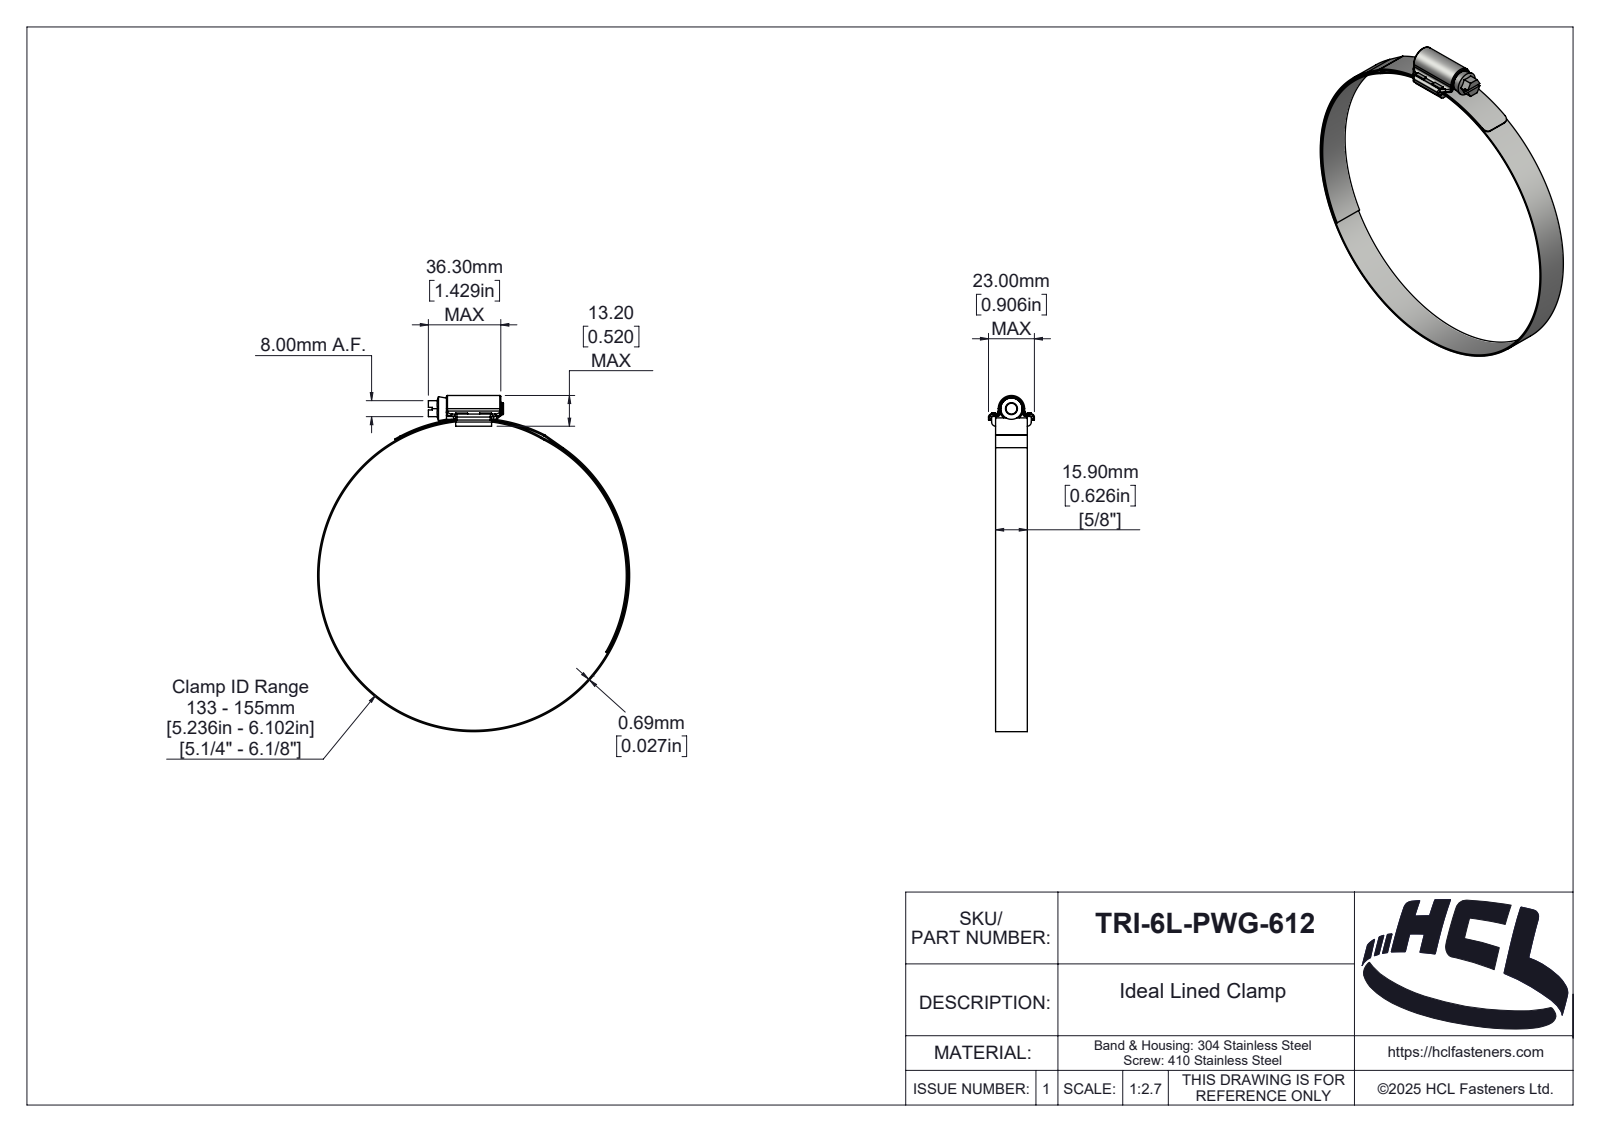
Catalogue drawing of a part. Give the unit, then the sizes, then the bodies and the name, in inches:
Units: inches
Overall size (bounding box): 6.63 × 6.157 × 0.906
Round holes (diameter × count): ⌀6.102 ×1
Round bosses / shafts (diameter × count): ⌀6.157 ×1, ⌀0.421 ×1, ⌀0.236 ×1
Partial cylindrical surfaces — rounded edges, fillets, slot ends (radius × count): R0.039 ×14, R0.02 ×4, R0.059 ×4, R0.079 ×3, R0.004 ×2, R0.083 ×2, R0.118 ×2, R0.018 ×1
Main face-to-face distances: 0.626, 0.079, 0.705, 0.027, 0.193, 0.047, 0.179, 0.132, 0.604, 0.1
Volume: 0.78 in³ · Surface area: 42.72 in²
Bodies: 4 solids, 268 faces (87 planar, 102 cylindrical, 79 other)
Part name (STEP PRODUCT): TRI-6L-PWG-612
STEP written by: SolidWorks 2025 (AUTOMOTIVE_DESIGN)
